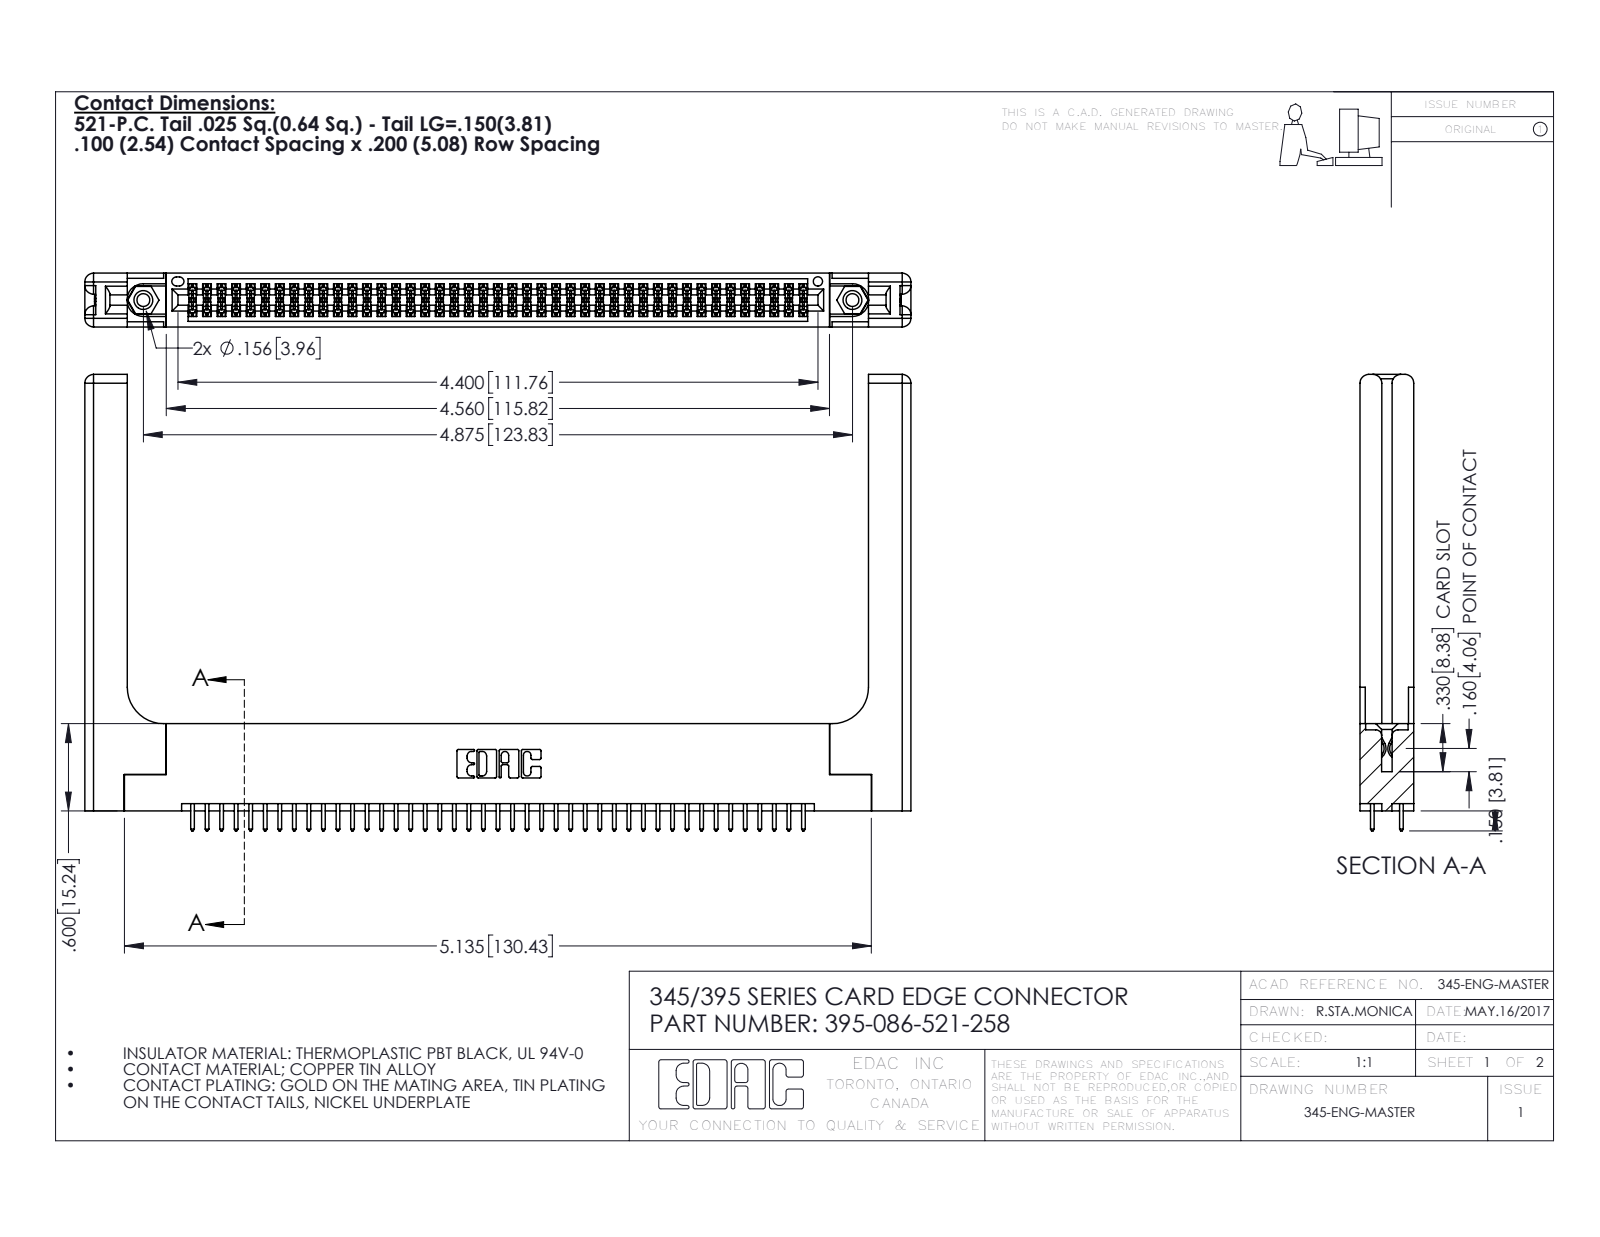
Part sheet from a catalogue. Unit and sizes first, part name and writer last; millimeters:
Units: millimetres
Overall size (bounding box): 144.2 × 79.7 × 9.4
Round holes (diameter × count): ⌀2.3 ×2, ⌀3.2 ×2, ⌀4 ×2, ⌀1.6 ×1
Round bosses / shafts (diameter × count): ⌀3.9 ×2
Partial cylindrical surfaces — rounded edges, fillets, slot ends (radius × count): R0.2 ×129, R0.3 ×86, R0.3 ×22, R1.5 ×16, R0.2 ×6, R0.8 ×6, R0.7 ×3, R0.4 ×2
Main face-to-face distances: 1.8, 7.6, 9.4, 5.1, 2.5, 6.9, 0.6, 5.7, 3.8, 3.8
Hole centre spacings: 6.9, 117.8, 123.8
Volume: 22 470 mm³ · Surface area: 25 520 mm²
Bodies: 91 solids, 4682 faces (3066 planar, 1556 cylindrical, 60 other)
Part name (STEP PRODUCT): 345-250-001_345-250-001-102; 345-292-001_345-293-121; 395-086-521-258; 345 Part_Flush Mounting Lugs - 0.156 Dia-TH (+1 more)
STEP written by: SolidWorks 2016 (CONFIG_CONTROL_DESIGN)
